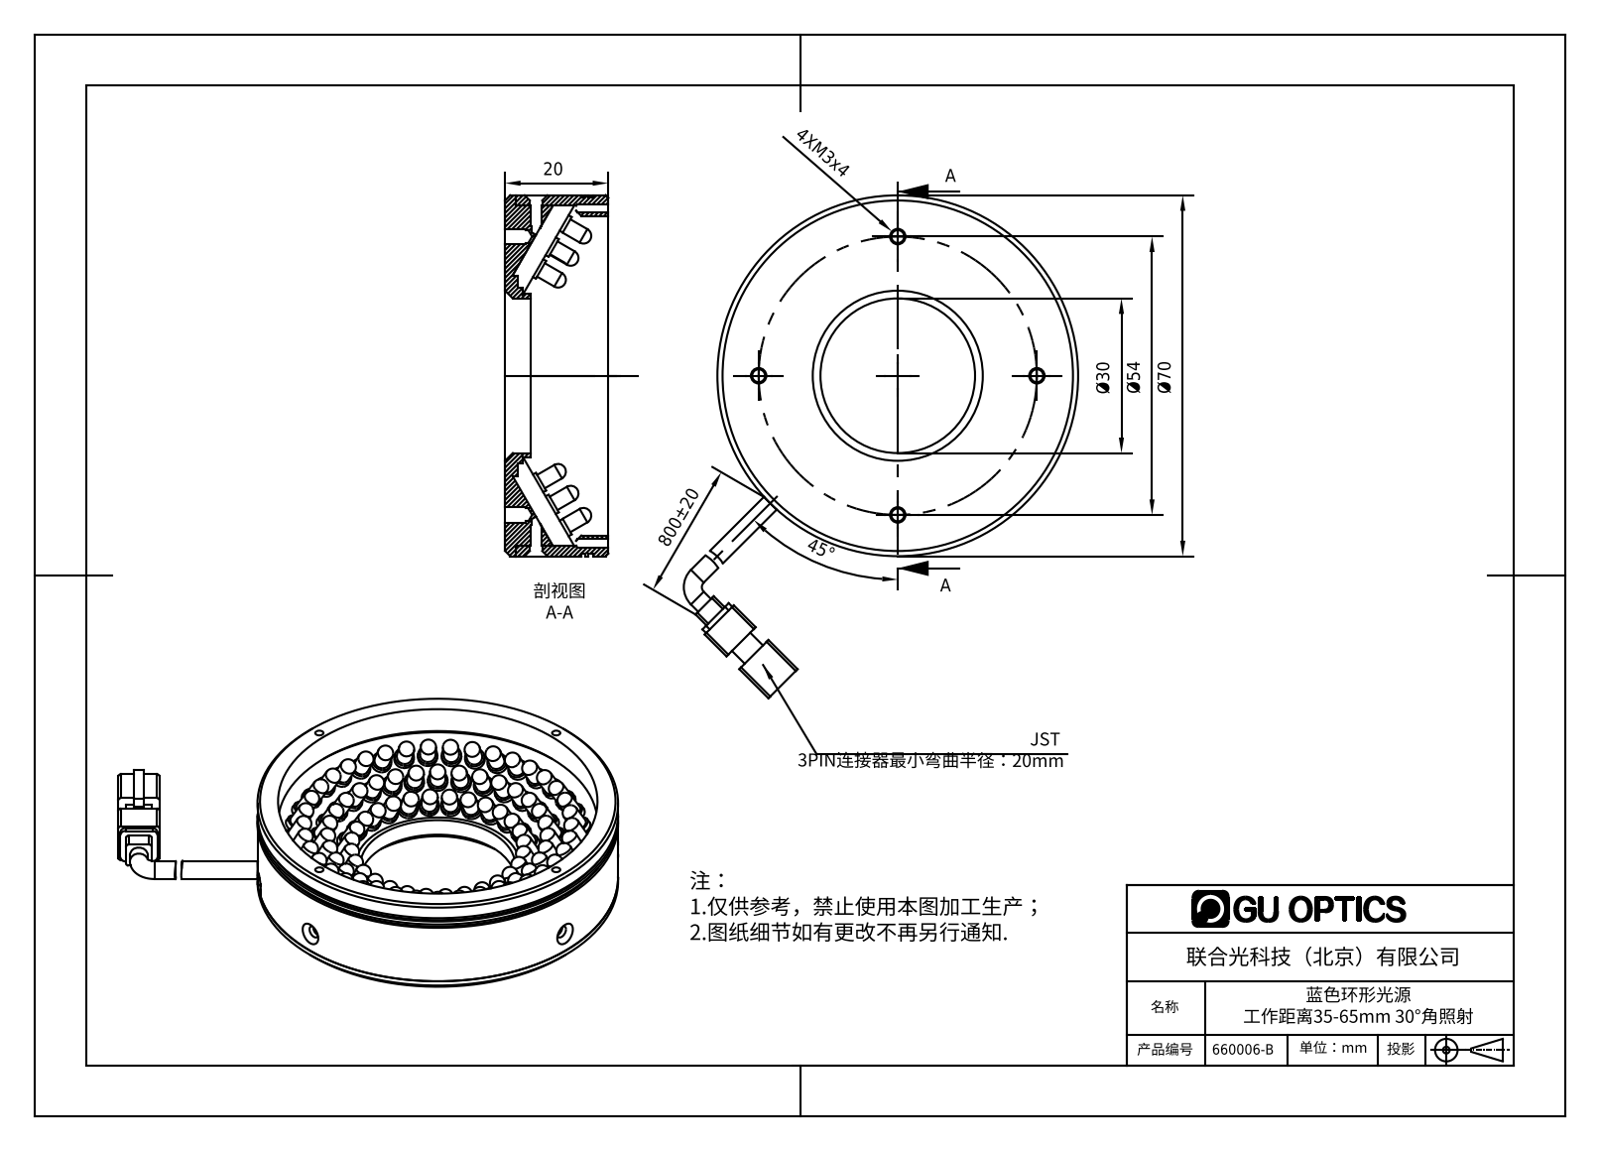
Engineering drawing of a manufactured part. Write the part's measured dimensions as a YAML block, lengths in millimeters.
part_name: "660006-B"
step_written_by: "SolidWorks 2016 (AUTOMOTIVE_DESIGN)"
units: millimeters
bodies: {solids: 103, faces: 1954, planar: 1269, cylindrical: 520, other: 165}
overall_size: [97.58, 76.52, 20.3]
volume: 29887
surface_area: 34722
round_holes:
  - {diameter: 3, count: 7}
  - {diameter: 1.6, count: 6}
  - {diameter: 2.5, count: 4}
  - {diameter: 2, count: 2}
  - {diameter: 2.4, count: 2}
  - {diameter: 30, count: 1}
  - {diameter: 62, count: 1}
round_bosses_or_shafts:
  - {diameter: 3.8, count: 98}
  - {diameter: 3, count: 96}
  - {diameter: 3.5, count: 2}
  - {diameter: 70, count: 1}
  - {diameter: 69, count: 1}
  - {diameter: 66, count: 1}
  - {diameter: 38.84, count: 1}
  - {diameter: 34, count: 1}
partial_cylinders:
  - {radius: 0.5, count: 8}
  - {radius: 1.6, count: 6}
  - {radius: 1, count: 4}
  - {radius: 9, count: 1}
face_to_face_distances: [2, 20, 18, 1, 0.5, 1.5, 3, 2.44, 0.44, 17.56]
hole_center_spacings: [42.25, 5.5, 27, 32.5, 38.18, 45.96, 59.5, 54]
